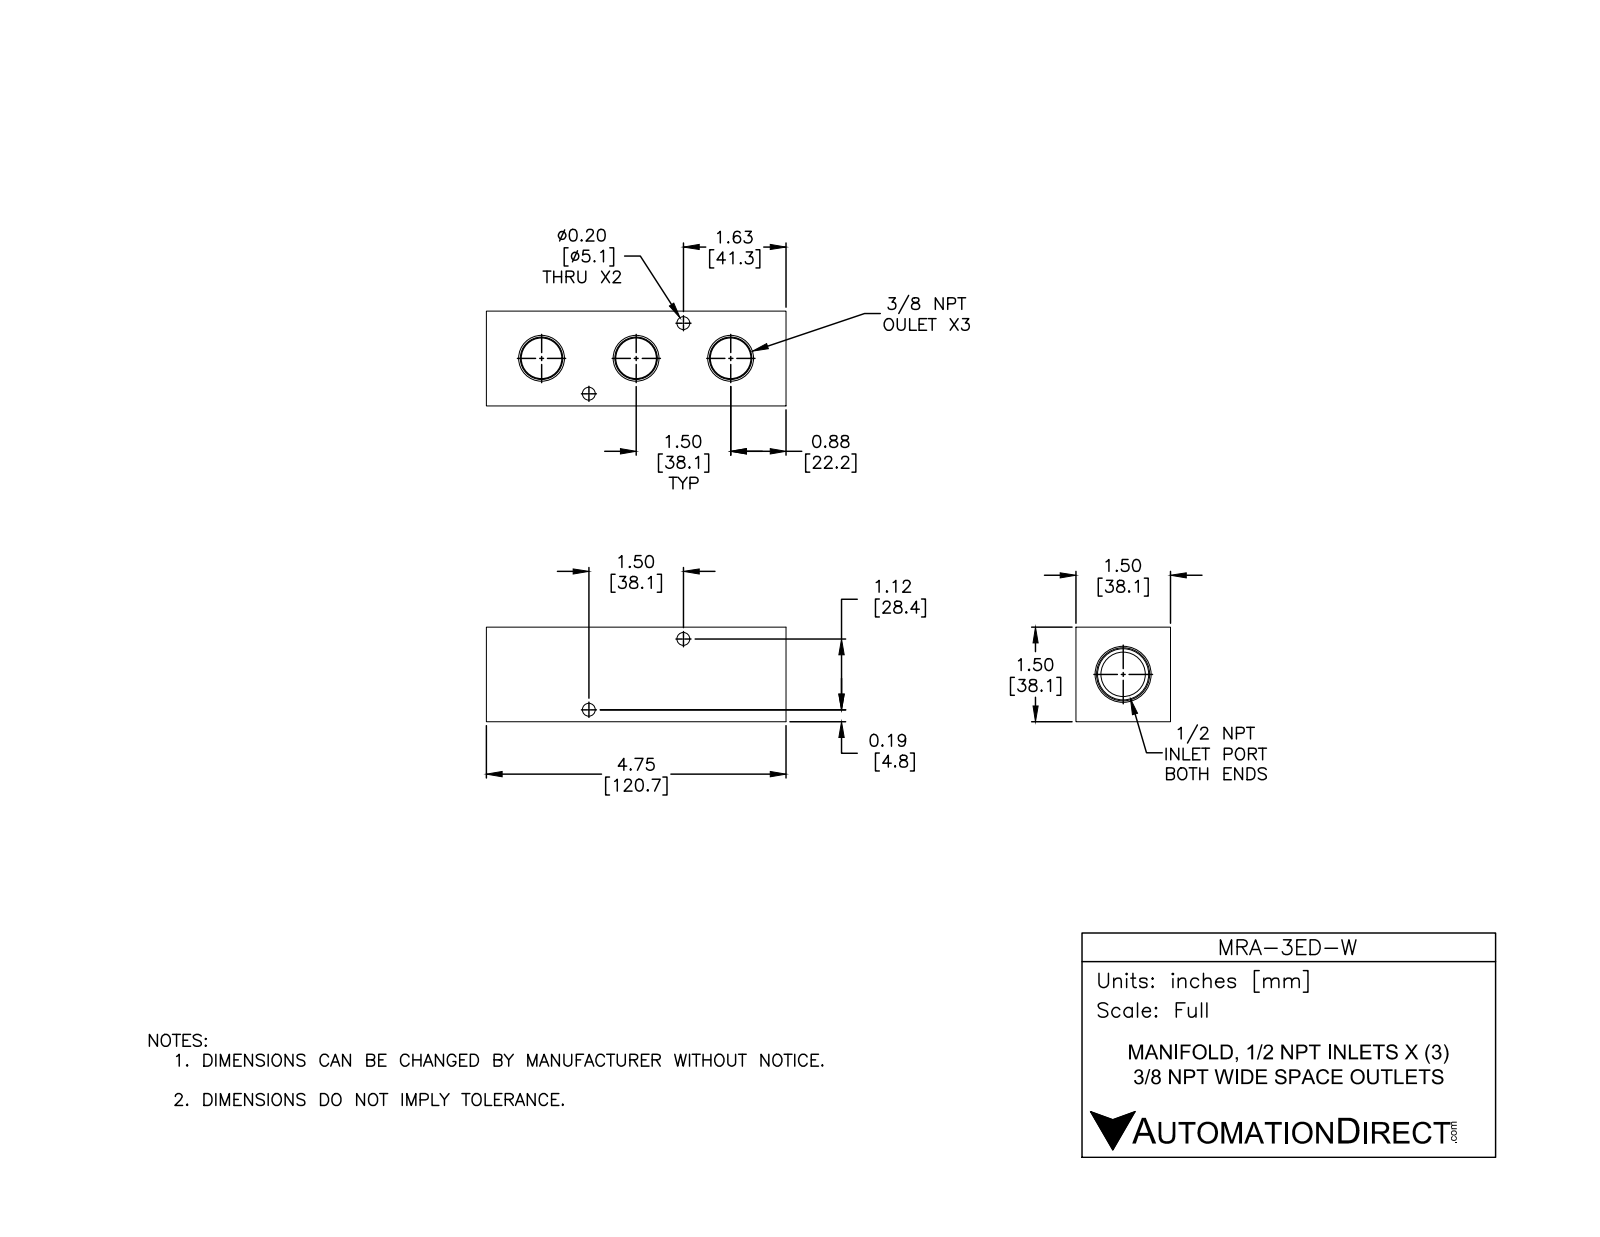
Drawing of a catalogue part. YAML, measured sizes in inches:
part_name: "MRA-3ED-W"
step_written_by: "SolidWorks 2015 (CONFIG_CONTROL_DESIGN)"
units: inches
bodies: {solids: 1, faces: 58, planar: 14, cylindrical: 24, other: 20}
overall_size: [4.75, 1.5, 1.5]
volume: 8.066
surface_area: 47.19
round_holes:
  - {diameter: 0.2, count: 4}
  - {diameter: 0.562, count: 3}
  - {diameter: 0.703, count: 1}
face_to_face_distances: [1.5, 4.75, 0.53, 4.22, 1.09, 0.41, 3.69]
hole_center_spacings: [0.932, 0.94, 1.5, 1.872, 2.314, 2.324, 3]
